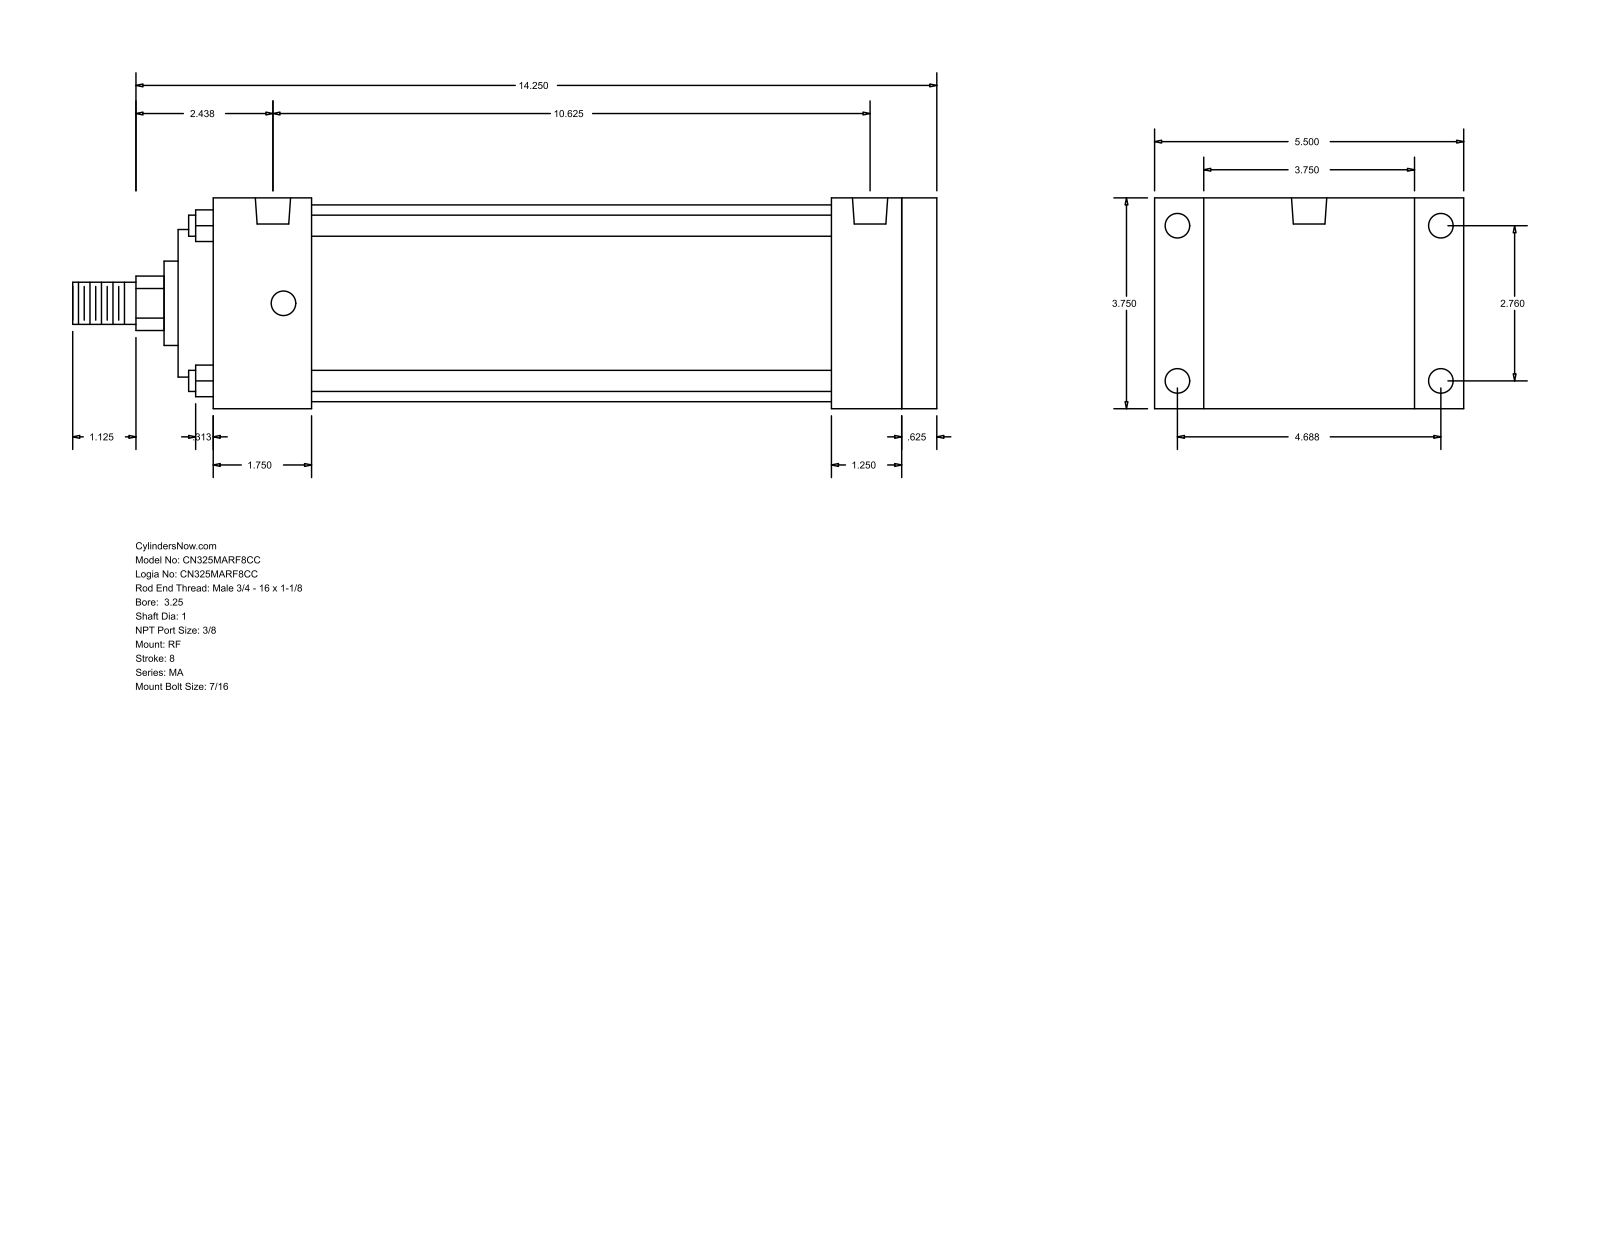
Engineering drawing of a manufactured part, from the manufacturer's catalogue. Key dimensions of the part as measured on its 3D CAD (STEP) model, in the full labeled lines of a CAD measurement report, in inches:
Part name (STEP PRODUCT): MA_RF__0325_1
STEP written by: GSSL Pune (CONFIG_CONTROL_DESIGN)
Units: inches
Bodies: 0 solids, 94 faces (65 planar, 29 cylindrical, 0 other)
Overall size (bounding box): 15.375 × 5.5 × 3.75
Round holes (diameter × count): ⌀0.437 ×8, ⌀0.627 ×2
Round bosses / shafts (diameter × count): ⌀0.375 ×4, ⌀3.5 ×1, ⌀2.625 ×1, ⌀1.5 ×1, ⌀1 ×1, ⌀0.75 ×1
Partial cylindrical surfaces — rounded edges, fillets, slot ends (radius × count): R0.484 ×1
Main face-to-face distances: 3.75, 12.875, 12.25, 0.625, 0.875, 4.625, 11, 1.25, 1.875, 1.75
Hole centre spacings: 2.76, 4.687, 5.439, 10.25, 0.187, 0.188, 10.437, 10.438
